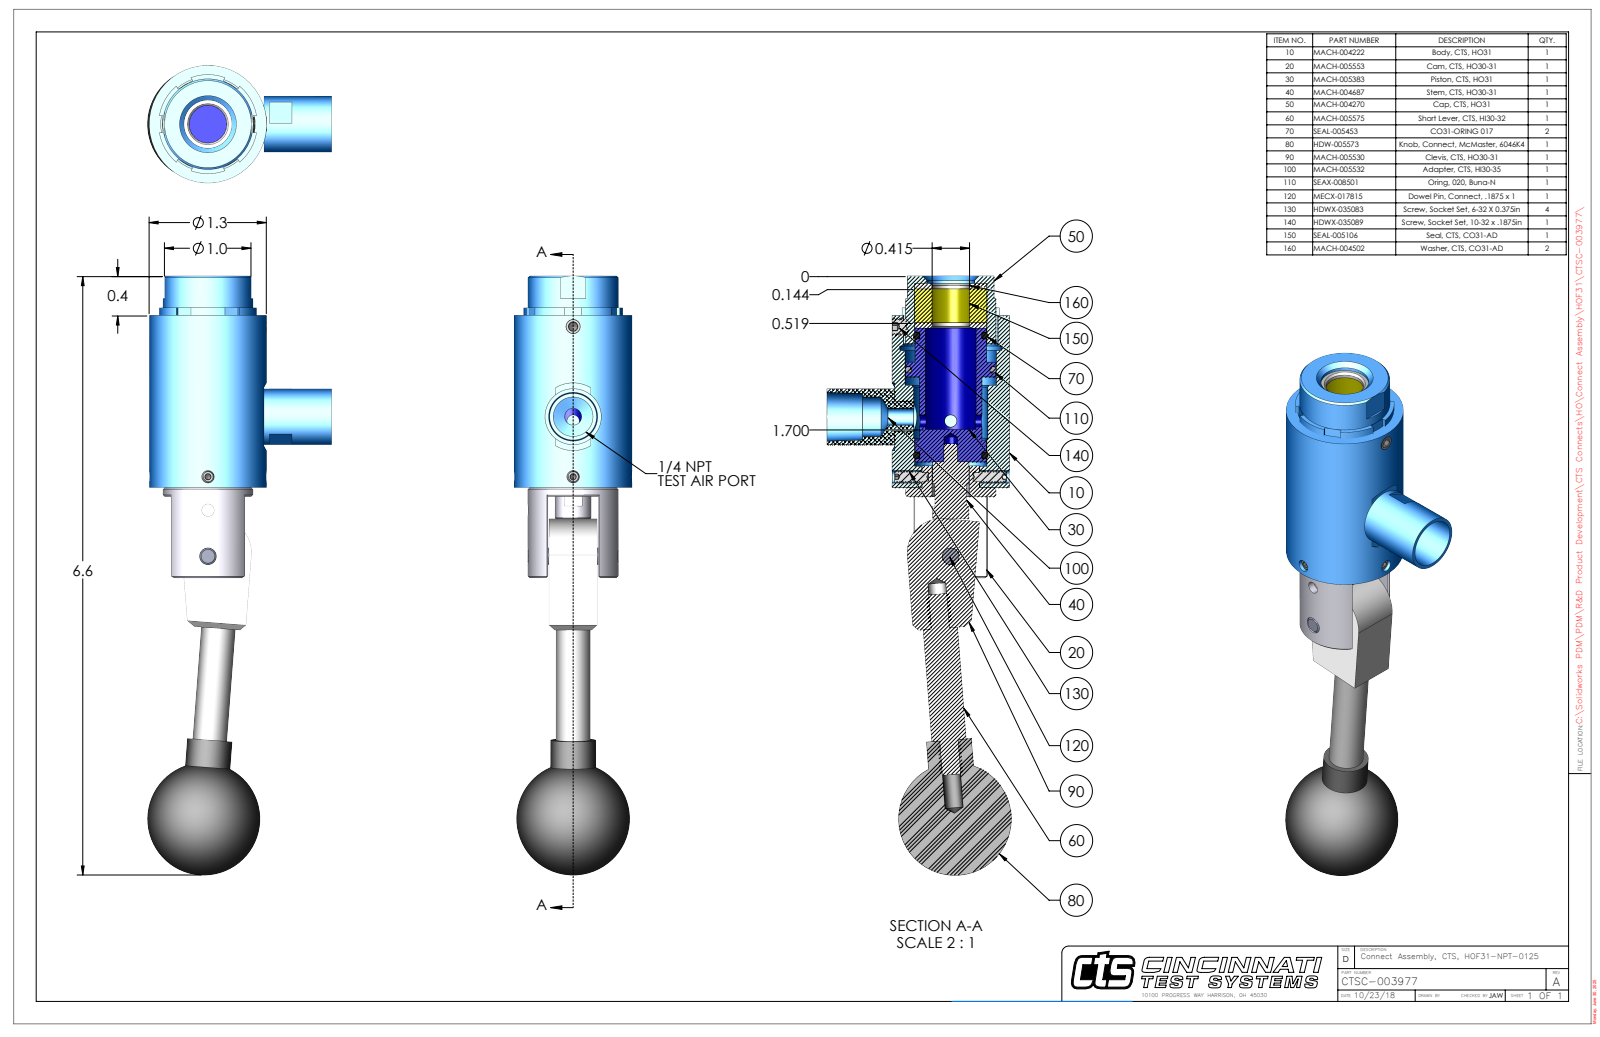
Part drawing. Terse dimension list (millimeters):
name: CTSC-003977
written by: SolidWorks 2023 (AUTOMOTIVE_DESIGN)
unit: mm
bodies: 14 solids, 532 faces (173 planar, 217 cylindrical, 142 other)
size: 168.6 × 51.9 × 33
volume: 73 990 mm³; area: 29 920 mm²
holes: 2× ⌀3.5, 2× ⌀5.1, 1× ⌀3.5, 1× ⌀3.8, 1× ⌀4, 1× ⌀4.7, 1× ⌀4.8, 1× ⌀4.8, 1× ⌀8.4, 1× ⌀10.5, 1× ⌀10.6, 1× ⌀10.6
bosses: 2× ⌀3.5, 1× ⌀33, 1× ⌀25.4, 1× ⌀20.1, 1× ⌀20.1, 1× ⌀17.5, 1× ⌀16, 1× ⌀15.7
rounds: 1× R9.5, 1× R9.5, 1× R13.3, 1× R13.9
face distances: 0.3, 13.8, 1.5, 11, 13.5, 9.5, 14.1, 46.4, 55.9, 57.4
hole spacings: 1.2, 13, 25.1, 25.3, 26.5, 38
